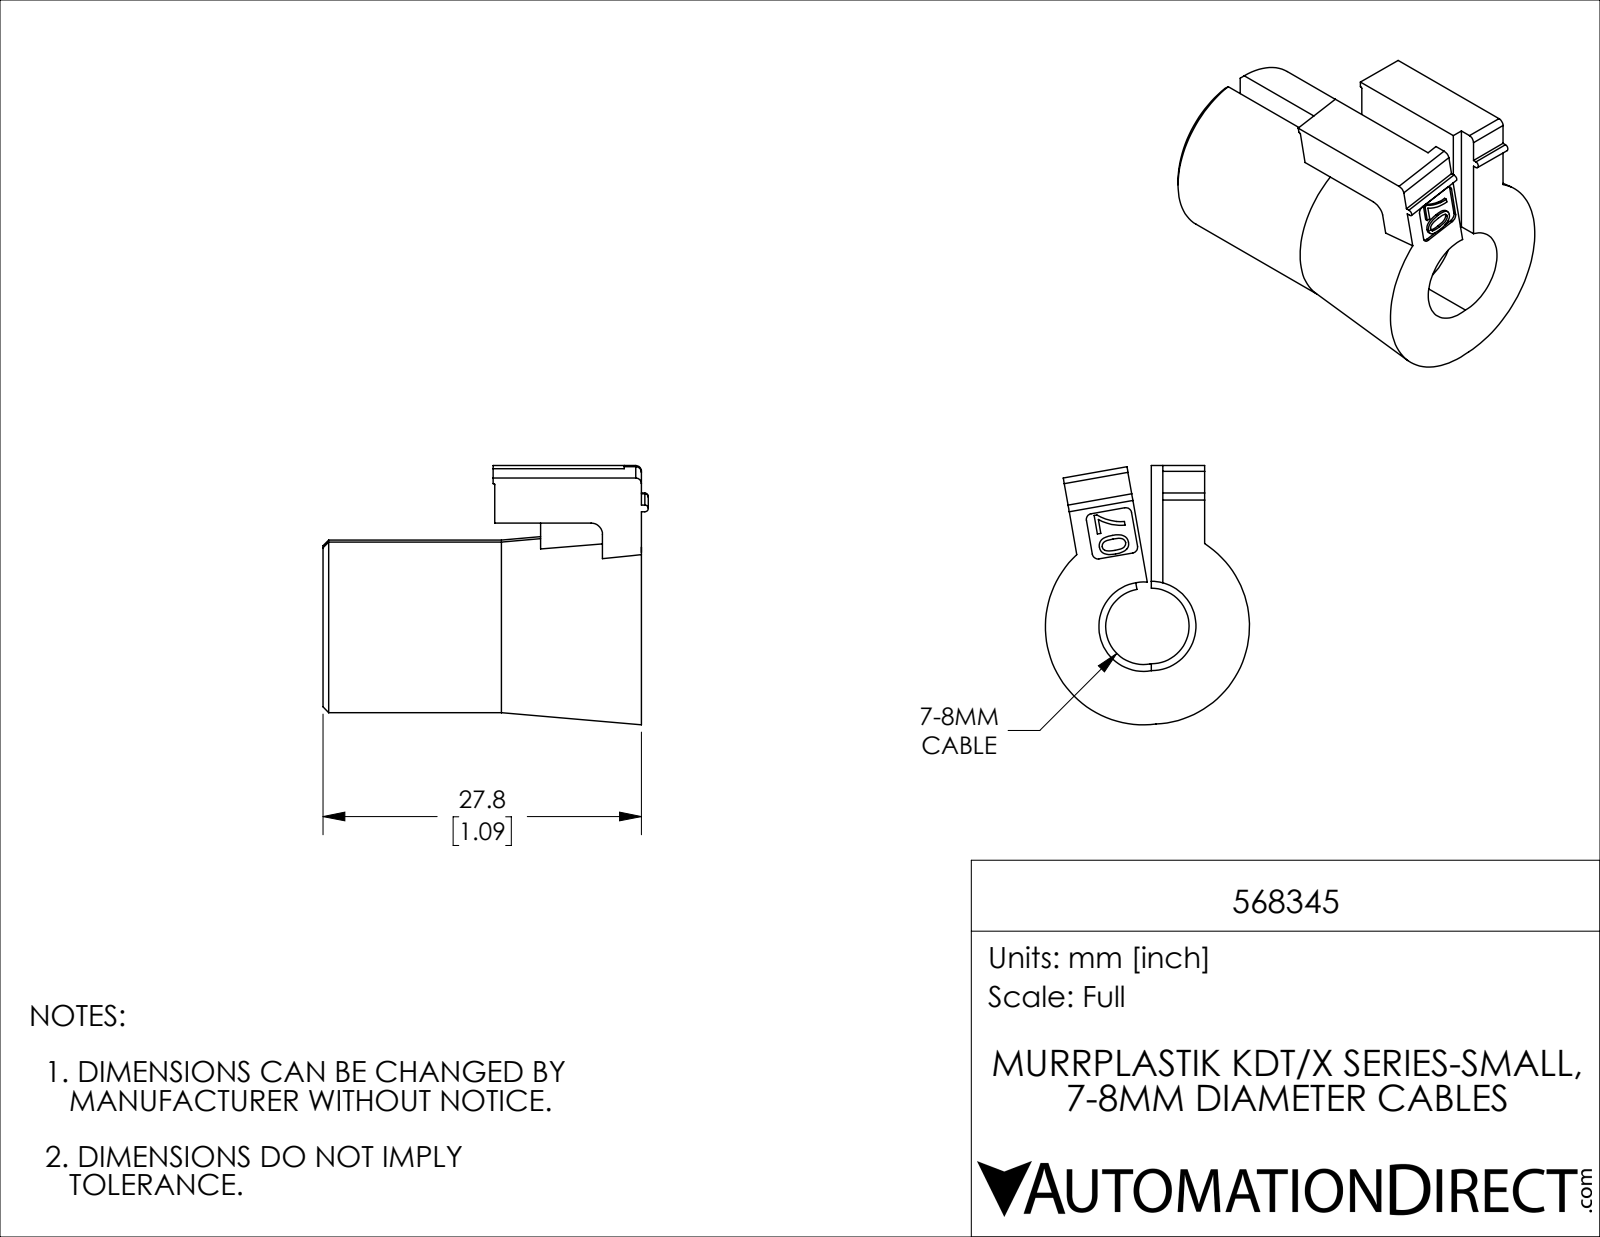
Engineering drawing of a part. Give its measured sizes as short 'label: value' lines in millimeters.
name: 568345
written by: SolidWorks 2019 (CONFIG_CONTROL_DESIGN)
unit: mm
bodies: 1 solid, 107 faces (57 planar, 24 cylindrical, 26 other)
size: 28.4 × 22.6 × 17.8
volume: 4 490 mm³; area: 3 086 mm²
rounds: 6× R0.5, 2× R0.1, 2× R0.3, 2× R1, 2× R3.3, 2× R3.9, 2× R7.5
face distances: 27.8, 4, 4.6, 4.6, 12.8, 15, 1.5, 11.3, 26.3, 1
